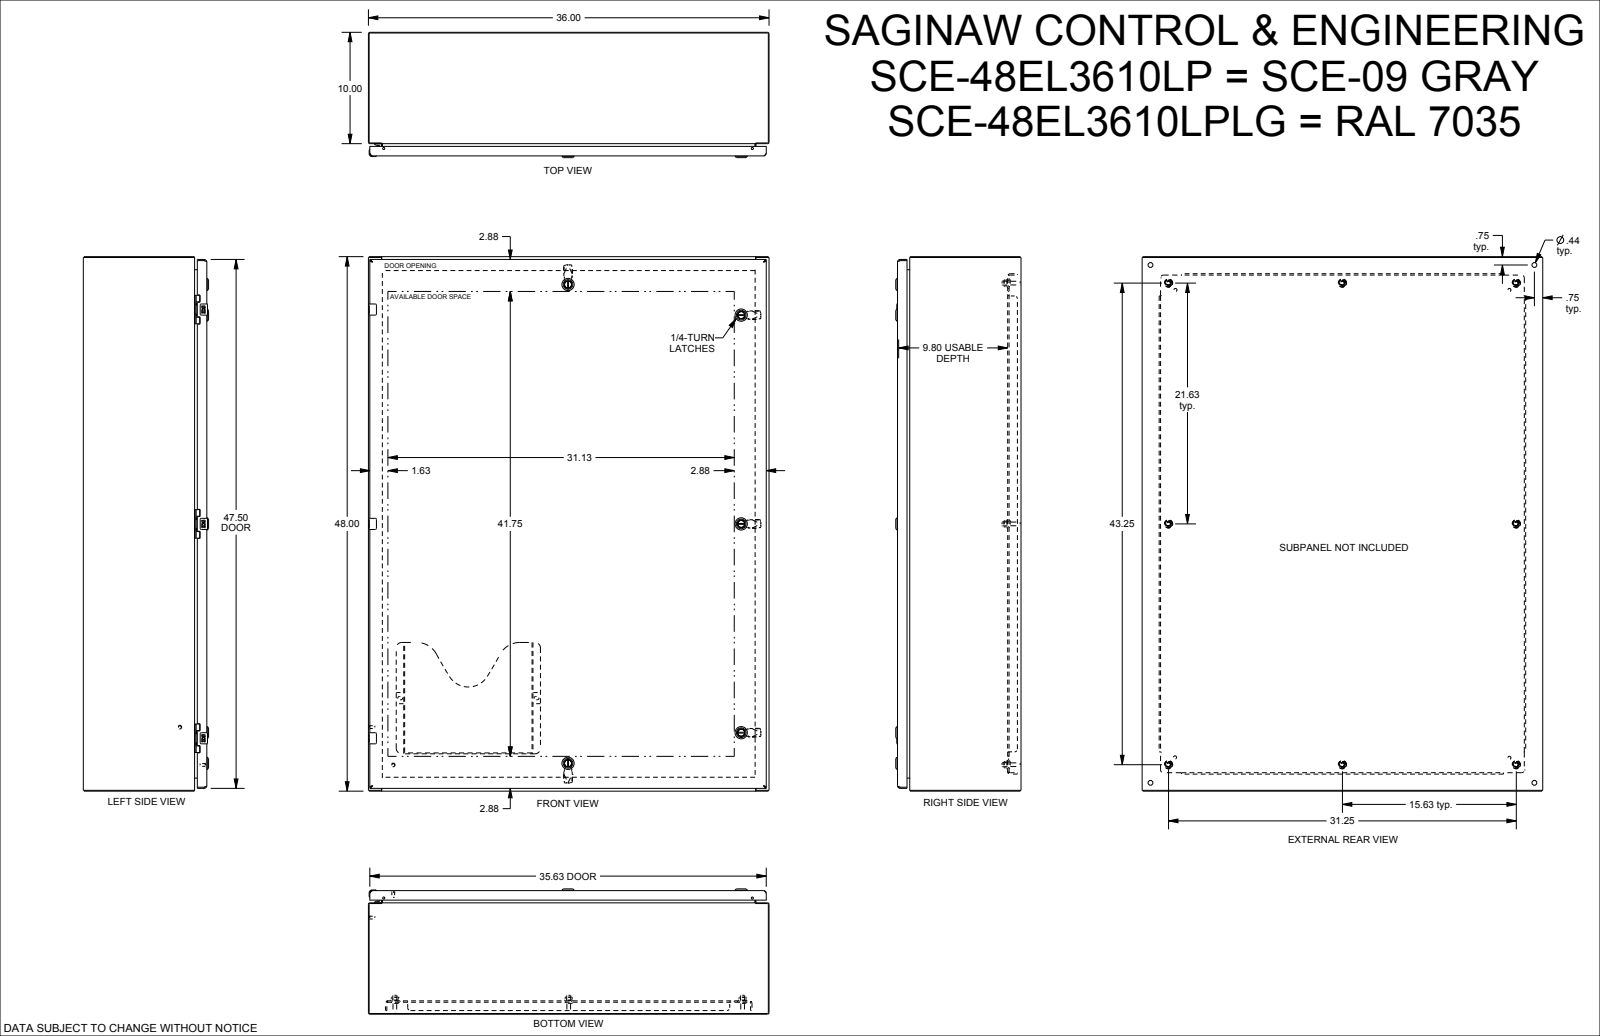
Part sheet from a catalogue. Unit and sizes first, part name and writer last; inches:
Units: inches
Overall size (bounding box): 48 × 36 × 11.256
Round holes (diameter × count): ⌀0.367 ×8, ⌀0.5 ×8, ⌀0.172 ×6, ⌀0.205 ×6, ⌀0.244 ×6, ⌀0.266 ×6, ⌀0.375 ×6, ⌀0.197 ×5, ⌀0.315 ×5, ⌀0.394 ×5, ⌀0.634 ×5, ⌀0.281 ×4
Round bosses / shafts (diameter × count): ⌀0.17 ×9, ⌀0.366 ×8, ⌀0.332 ×8, ⌀0.25 ×6, ⌀0.24 ×6, ⌀1.102 ×5, ⌀0.866 ×5, ⌀0.802 ×5
Partial cylindrical surfaces — rounded edges, fillets, slot ends (radius × count): R0.012 ×136, R0.01 ×52, R0.02 ×52, R0.015 ×32, R0.157 ×20, R0.04 ×17, R0.025 ×16, R0.1 ×16
Main face-to-face distances: 0.075, 0.104, 10.92, 10.995, 11.099, 11.024, 1.125, 9.795, 1, 9.92
Hole centre spacings: 19.25, 38.5, 0.05, 0.493, 0.494, 0.986, 18.265, 18.757
Bodies: 0 solids, 4768 faces (2330 planar, 1319 cylindrical, 1119 other)
Part name (STEP PRODUCT): SCE-48EL3610LP
STEP written by: SolidWorks 2019 (CONFIG_CONTROL_DESIGN)
